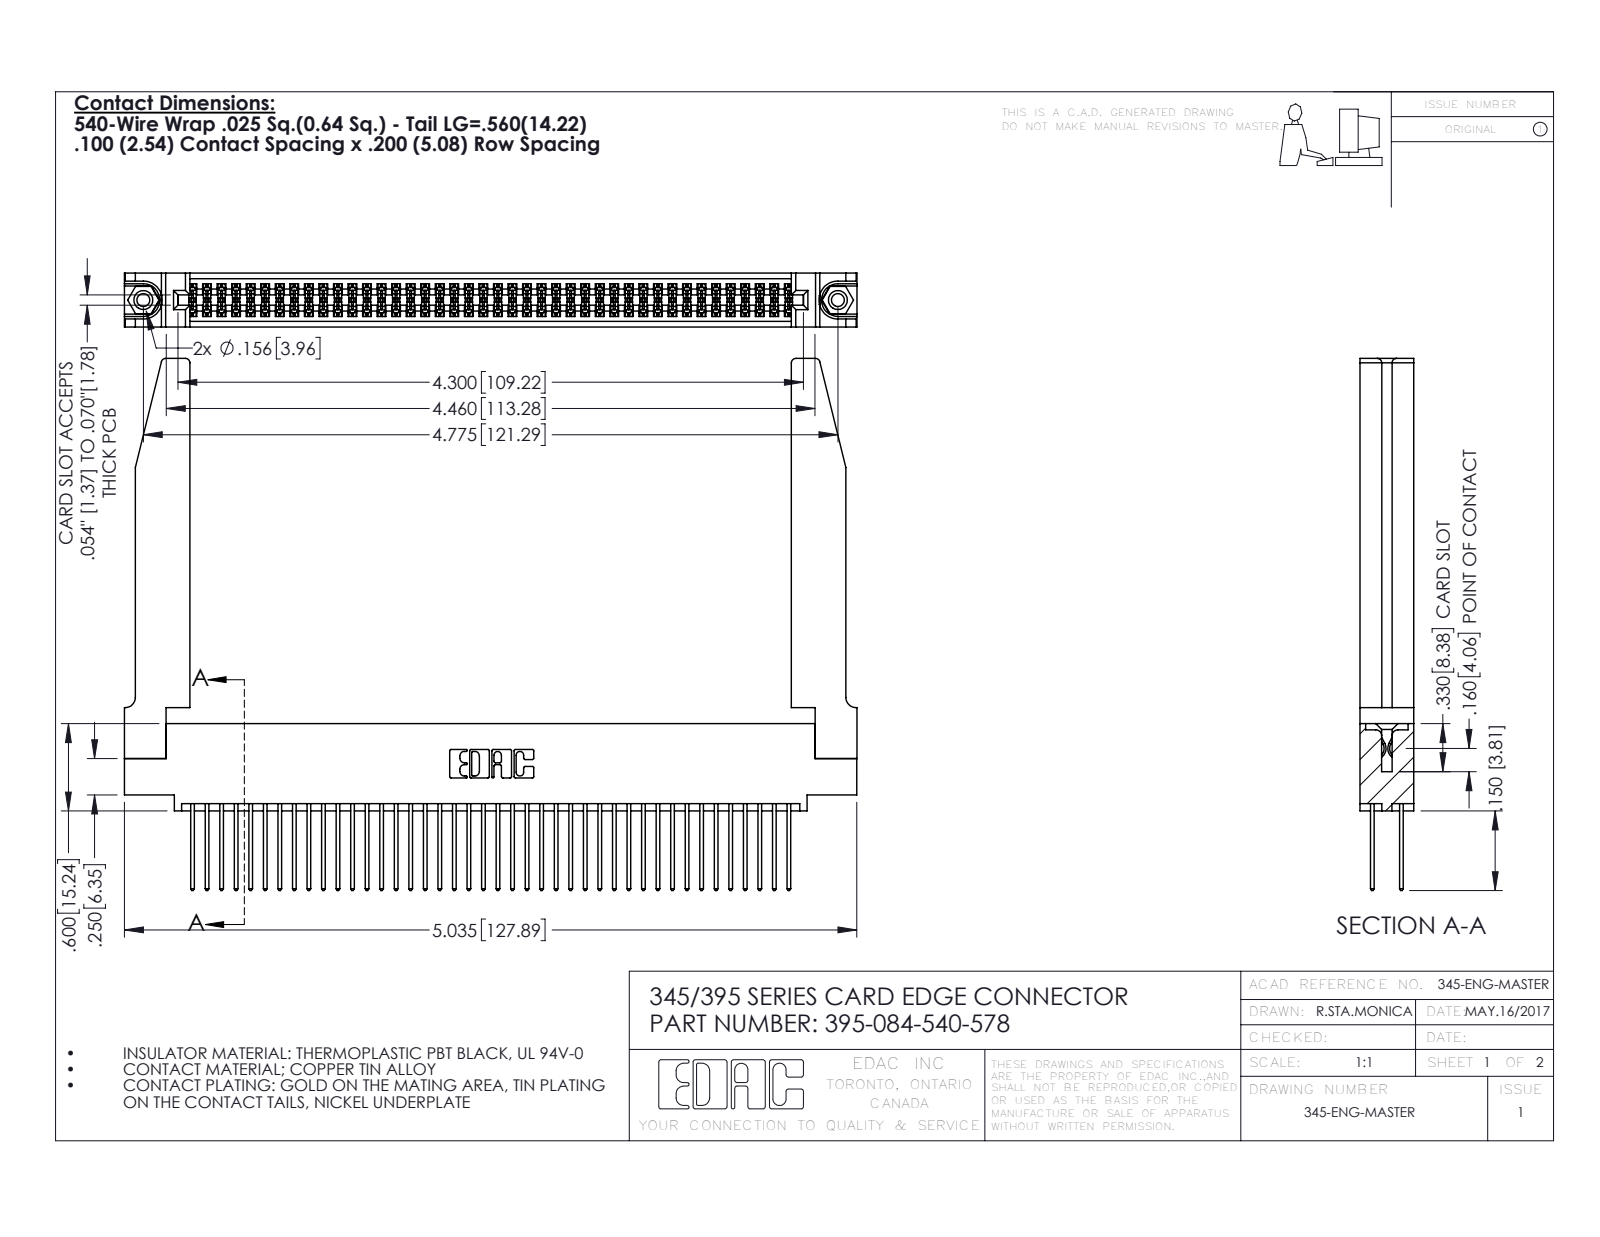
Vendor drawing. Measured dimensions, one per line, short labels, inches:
name: 345-220-078_345-220-078; 345-250-001_345-250-001-102; 345-292-001_345-293-140; 345 Part_0.110 Offset - 0.156 Dia-TH (+1 more)
written by: SolidWorks 2016 (CONFIG_CONTROL_DESIGN)
unit: in
bodies: 89 solids, 4564 faces (2998 planar, 1514 cylindrical, 52 other)
size: 5.036 × 3.657 × 0.37
volume: 1.247 in³; area: 42.06 in²
holes: 2× ⌀0.089, 2× ⌀0.125, 2× ⌀0.156, 1× ⌀0.064
bosses: 2× ⌀0.155
rounds: 126× R0.006, 84× R0.01, 22× R0.01, 8× R0.03, 6× R0.007, 6× R0.031, 3× R0.026, 2× R0.014
face distances: 0.072, 0.298, 0.37, 0.2, 0.098, 0.272, 0.025, 0.225, 0.175, 0.148
hole spacings: 0.27, 4.539, 4.775
